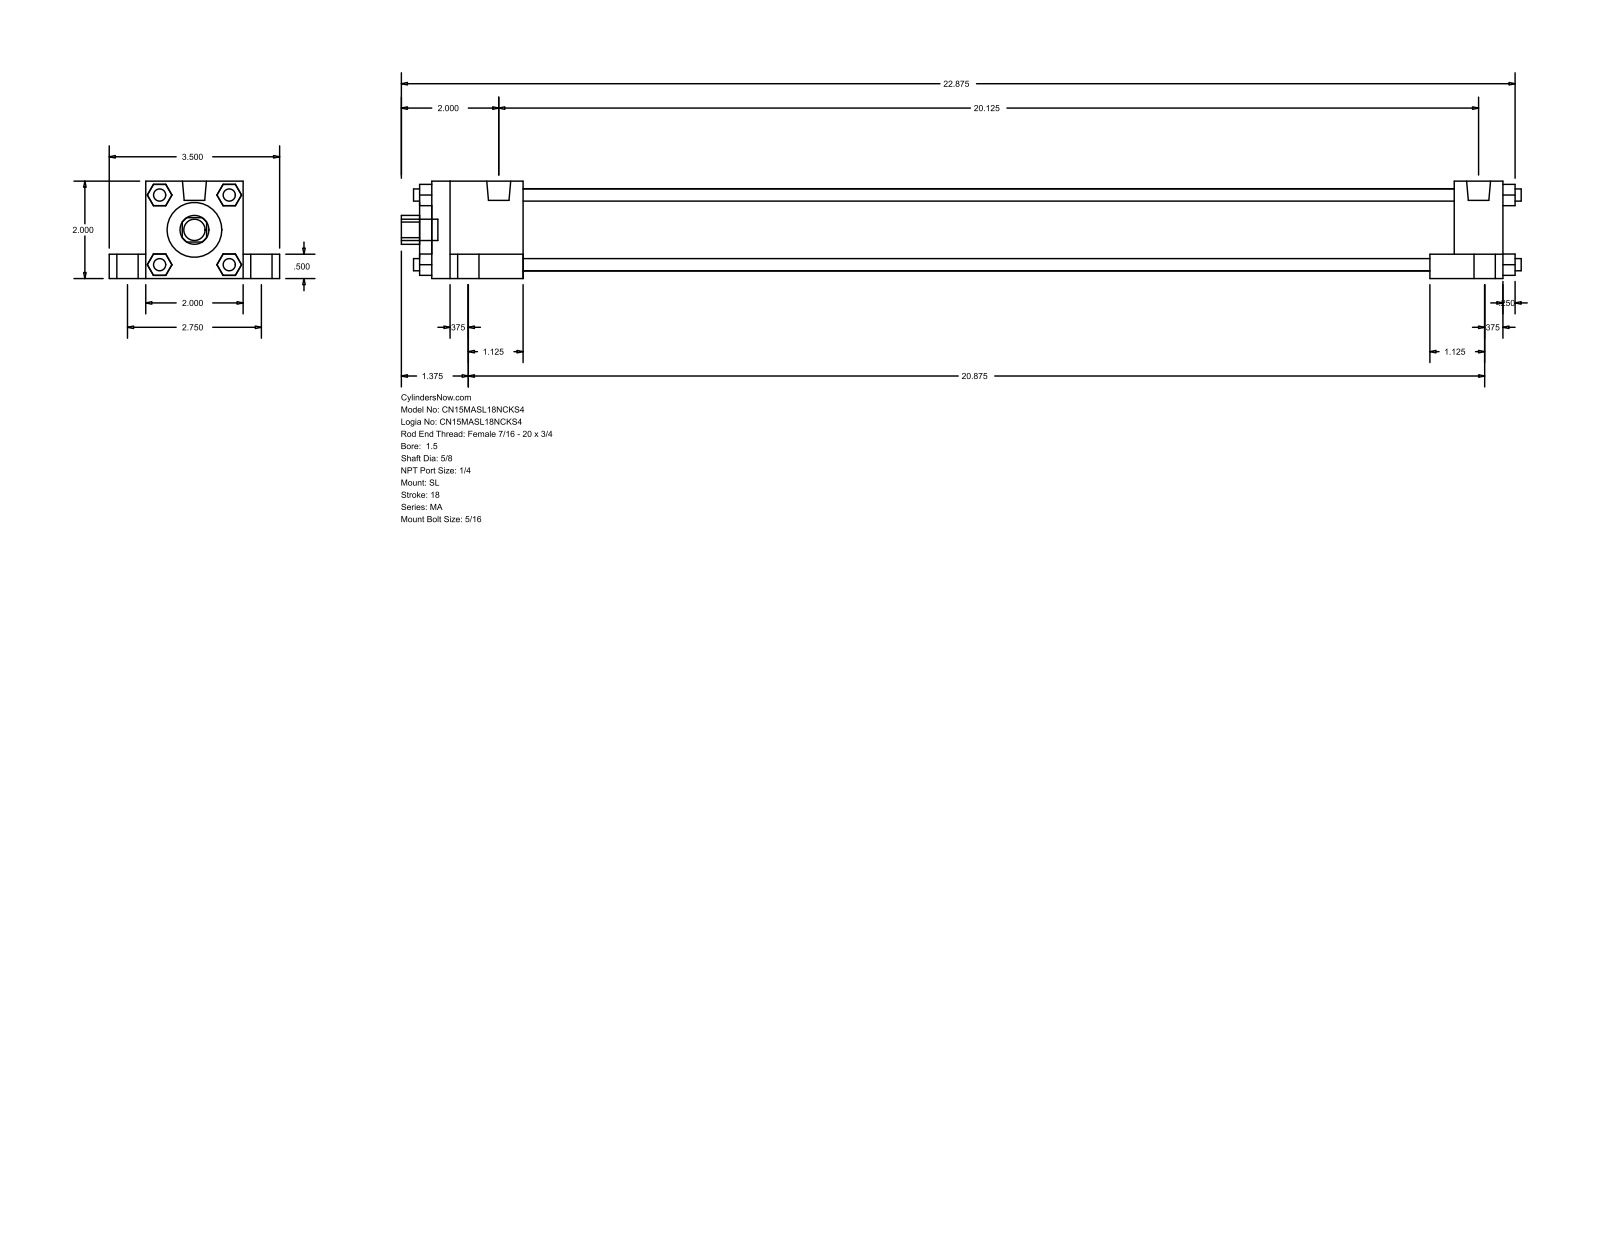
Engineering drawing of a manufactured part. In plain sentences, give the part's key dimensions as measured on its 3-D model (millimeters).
The part is named "MA_SL__0150_0.625". Its 3-D file was written by "GSSL Pune (CONFIG_CONTROL_DESIGN)". It is 0 solids with 148 faces: 112 planar, 36 cylindrical and 0 other. Overall it measures 584.2 by 88.9 by 50.8 millimeters. Round holes: 1 of diameter 15.88, 1 of diameter 28.57, 1 of diameter 42.93. Round bosses or shafts: 5 of diameter 11.11, 4 of diameter 17.46, 4 of diameter 7.94, 4 of diameter 6.35, 2 of diameter 12.49. Partial cylindrical surfaces (rounded edges, fillets, slot ends): 1 of radius 7.54. The main face-to-face distances are 50.8, 19.05, 38.1, 12.7, 69.85, 558.79, 485.77, 6.35, 9.52, 25.4.
